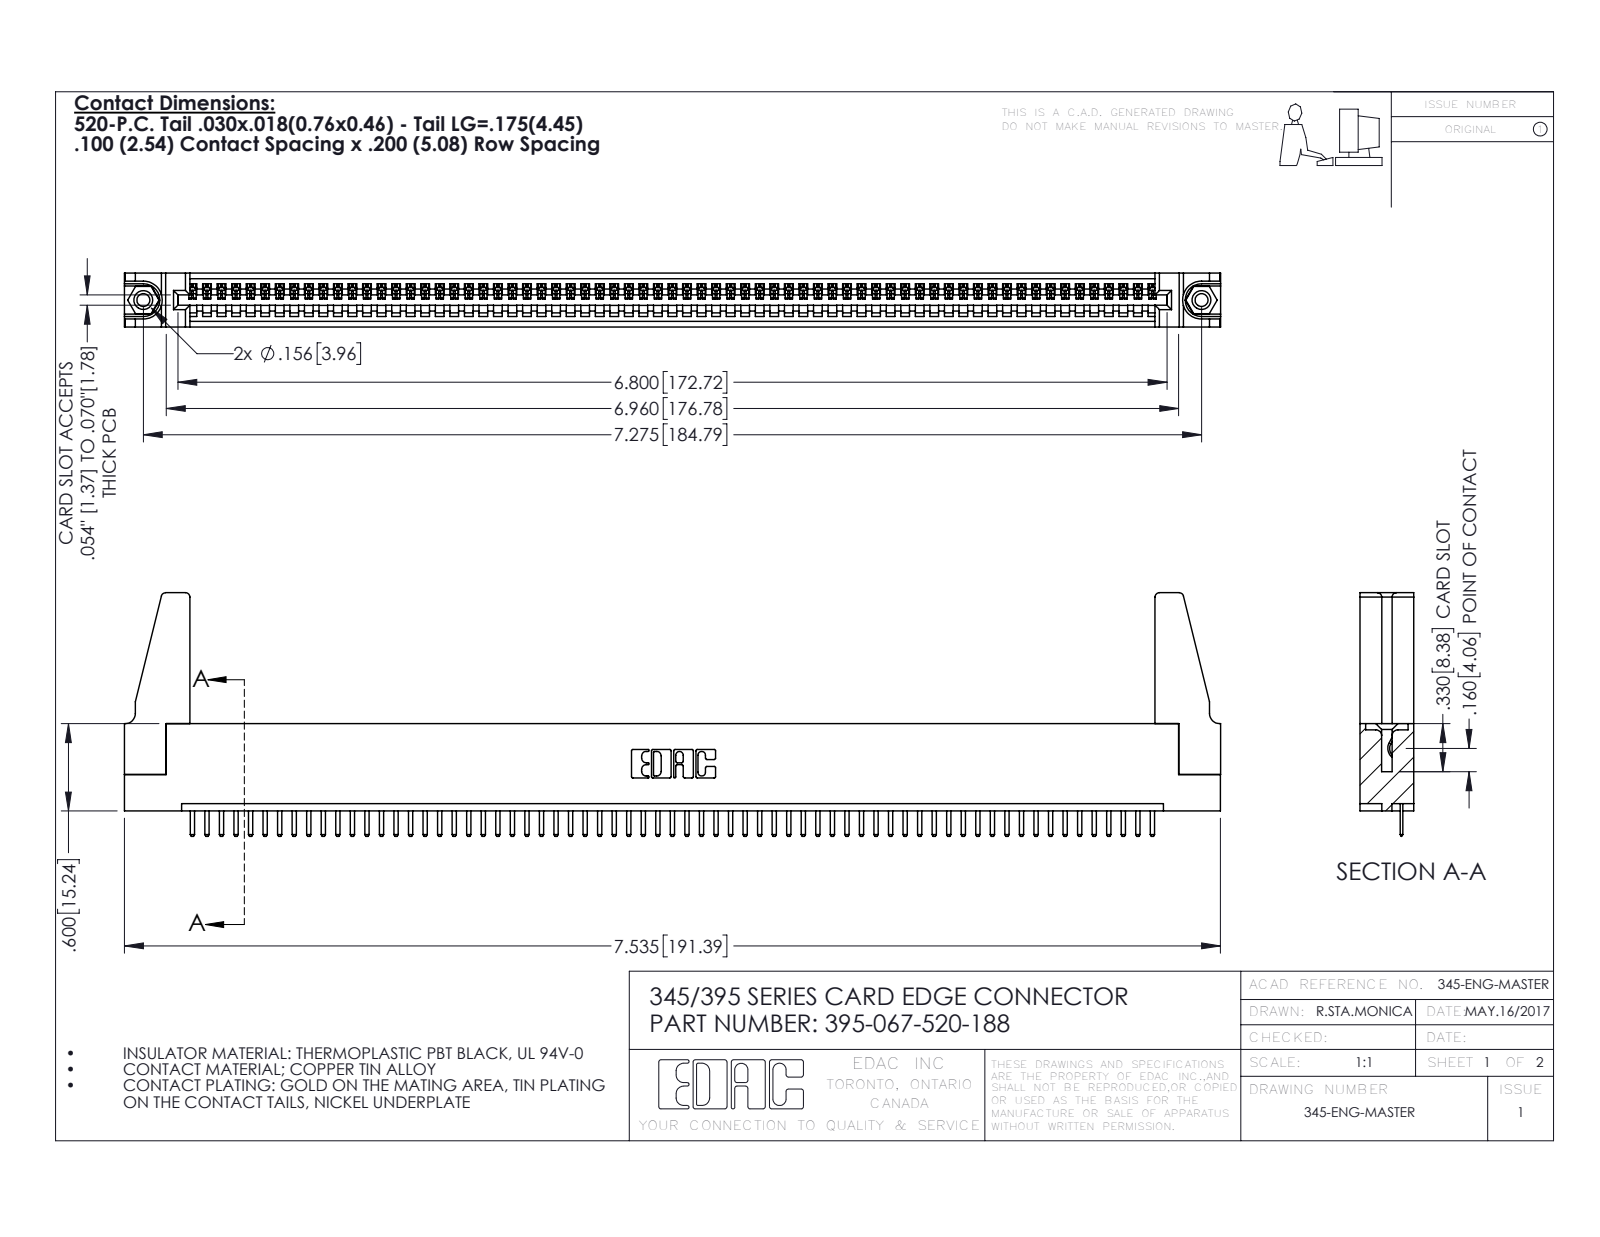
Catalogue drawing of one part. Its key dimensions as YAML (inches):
part_name: "345-292-001_345-293-120; 345 Part_Flush Mounting Lugs - 0.156 Dia-TH; 345-250-001_345-250-001-102; 395-067-520-188 (+1 more)"
step_written_by: "SolidWorks 2016 (CONFIG_CONTROL_DESIGN)"
units: inches
bodies: {solids: 72, faces: 4404, planar: 2966, cylindrical: 1422, other: 16}
overall_size: [7.536, 1.675, 0.37]
volume: 1.309
surface_area: 41.87
round_holes:
  - {diameter: 0.089, count: 2}
  - {diameter: 0.125, count: 2}
  - {diameter: 0.156, count: 2}
  - {diameter: 0.064, count: 1}
round_bosses_or_shafts:
  - {diameter: 0.155, count: 2}
partial_cylinders:
  - {radius: 0.01, count: 136}
  - {radius: 0.006, count: 134}
  - {radius: 0.01, count: 22}
  - {radius: 0.03, count: 8}
  - {radius: 0.007, count: 6}
  - {radius: 0.031, count: 6}
  - {radius: 0.026, count: 3}
  - {radius: 0.031, count: 2}
face_to_face_distances: [0.072, 0.298, 0.37, 0.2, 0.098, 0.272, 0.025, 0.225, 0.072, 0.149]
hole_center_spacings: [0.27, 7.039, 7.275]
